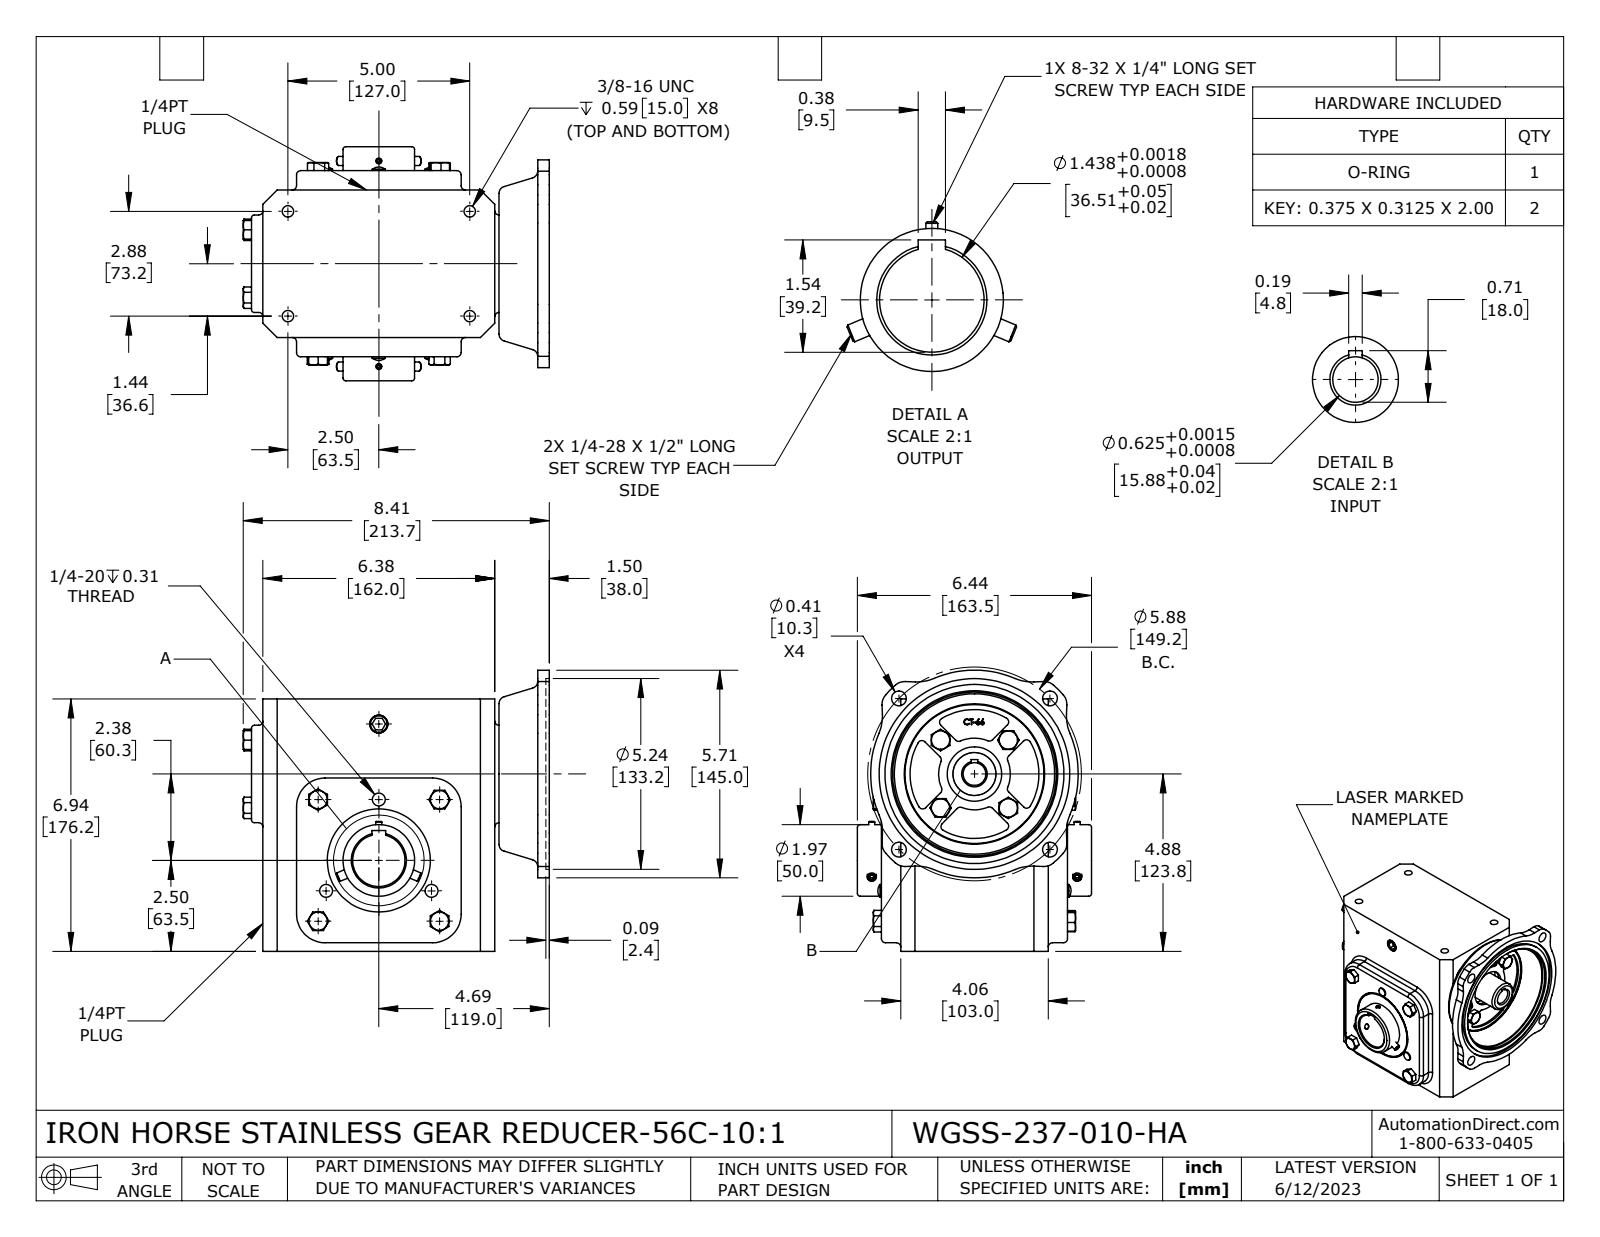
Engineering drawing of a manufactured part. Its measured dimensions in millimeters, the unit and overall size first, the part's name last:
Units: millimetres
Overall size (bounding box): 213.7 × 196.3 × 163.5
Round holes (diameter × count): ⌀5.4 ×4, ⌀8 ×4, ⌀10.3 ×4, ⌀3.5 ×2, ⌀15.9 ×1, ⌀22 ×1, ⌀36.5 ×1, ⌀36.6 ×1, ⌀38 ×1, ⌀45 ×1, ⌀97 ×1, ⌀114.3 ×1
Round bosses / shafts (diameter × count): ⌀6.4 ×4, ⌀9 ×3, ⌀4.2 ×2, ⌀125 ×1, ⌀72 ×1, ⌀50 ×1, ⌀30 ×1
Partial cylindrical surfaces — rounded edges, fillets, slot ends (radius × count): R3 ×40, R10 ×12, R30 ×8, R2 ×4, R20 ×4, R25 ×1, R45 ×1, R72.5 ×1
Main face-to-face distances: 13.5, 116.5, 176.2, 8, 103, 162, 130, 200, 30, 170
Hole centre spacings: 72.6, 74.6, 125.6, 143.5, 73.2, 105.5, 105.5, 127
Volume: 3 351 000 mm³ · Surface area: 224 600 mm²
Bodies: 7 solids, 670 faces (287 planar, 195 cylindrical, 188 other)
Part name (STEP PRODUCT): WGSS-237-010-HA
STEP written by: SolidWorks 2021 (CONFIG_CONTROL_DESIGN)
